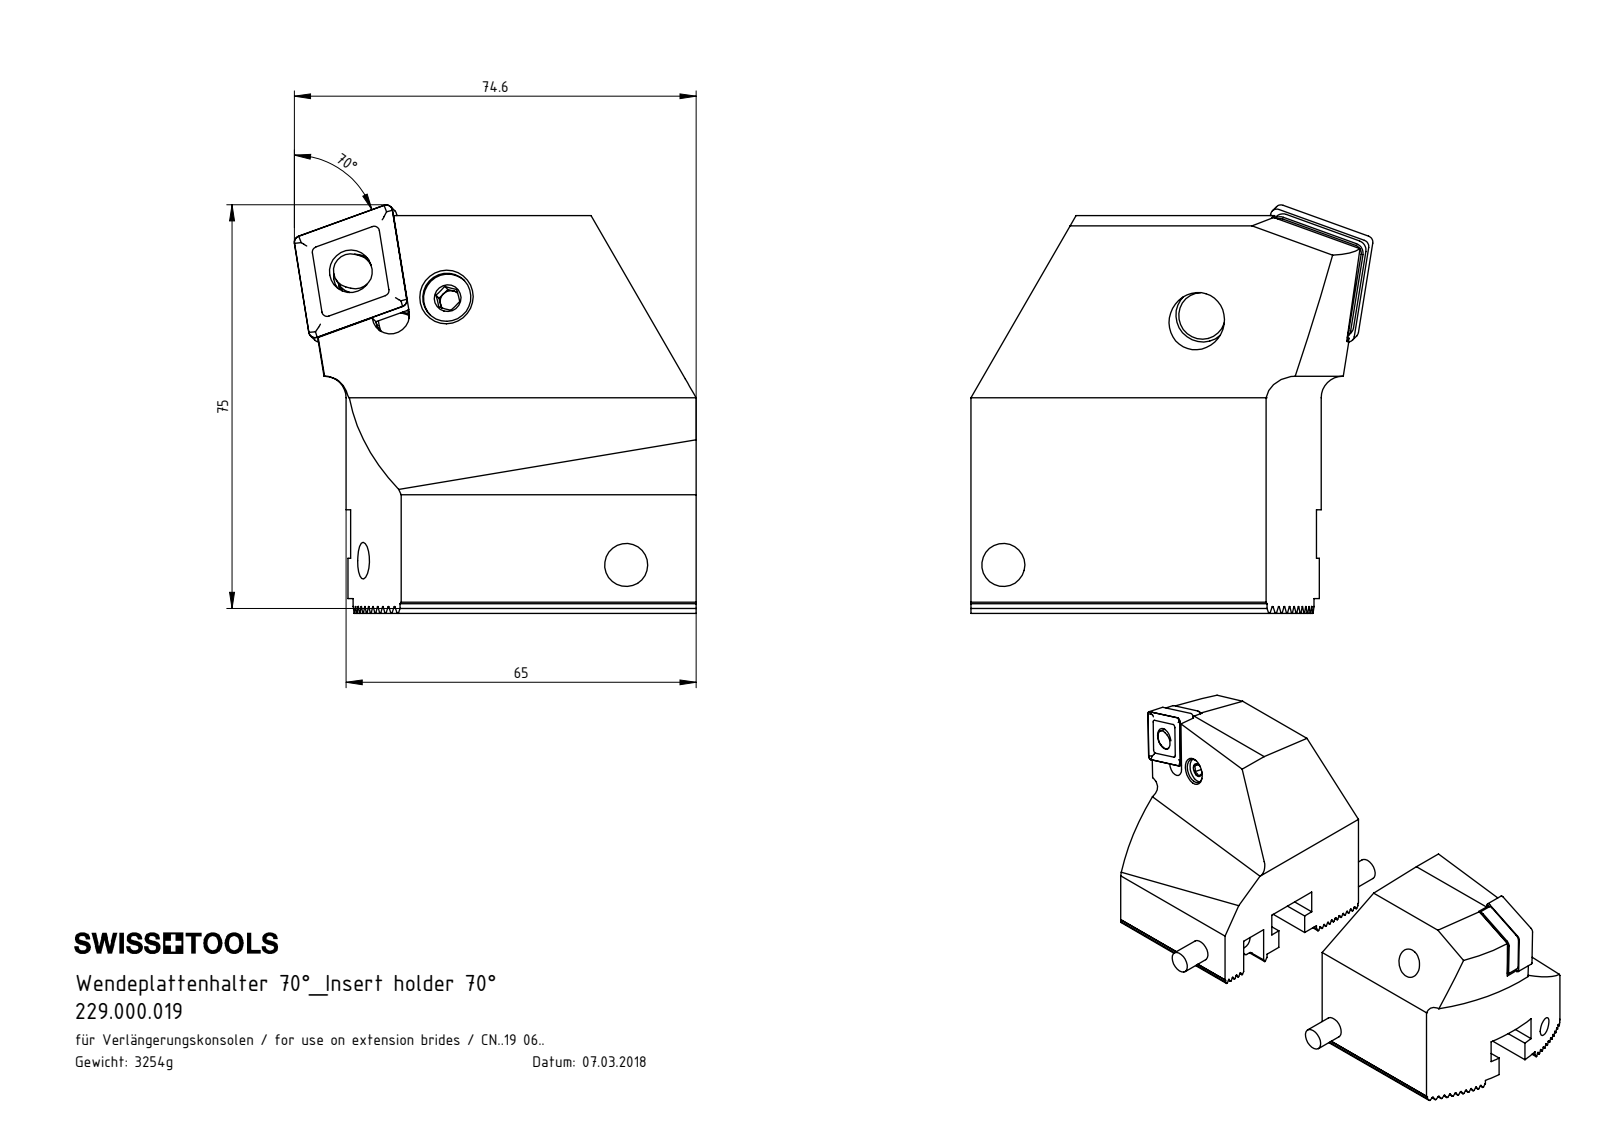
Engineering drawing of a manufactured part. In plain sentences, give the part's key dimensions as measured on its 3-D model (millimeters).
The part is named "229.000.019; WCF-ER3.101.000_A; WCF-ER4.101.027_A; VK1-WCF.102.075_A (+6 more)". Its 3-D file was written by "SolidWorks 2017 (CONFIG_CONTROL_DESIGN)". It is 18 solids with 1312 faces: 784 planar, 172 cylindrical and 356 other. Overall it measures 200.21 by 94 by 75.79 millimeters. Its volume is 411 183 cubic millimeters and its surface area 74 323 square millimeters. Round holes: 4 of diameter 8, 2 of diameter 6.8, 2 of diameter 7.94, 2 of diameter 9, 2 of diameter 9.6, 2 of diameter 10.2. Round bosses or shafts: 2 of diameter 10, 2 of diameter 9.9, 2 of diameter 8.6, 2 of diameter 8, 2 of diameter 5.5, 2 of diameter 4.45. Partial cylindrical surfaces (rounded edges, fillets, slot ends): 22 of radius 0.14, 8 of radius 1.2, 8 of radius 1.8, 8 of radius 4.15, 3 of radius 4.7, 2 of radius 3.1, 2 of radius 3.5, 2 of radius 3.65. The main face-to-face distances are 1.73, 6.93, 8.66, 70, 3.46, 5.2, 41.57, 43.3, 24.5, 45.5. The hole center spacings are 7, 18.55, 70, 18.8, 18.81, 40, 63, 77.
